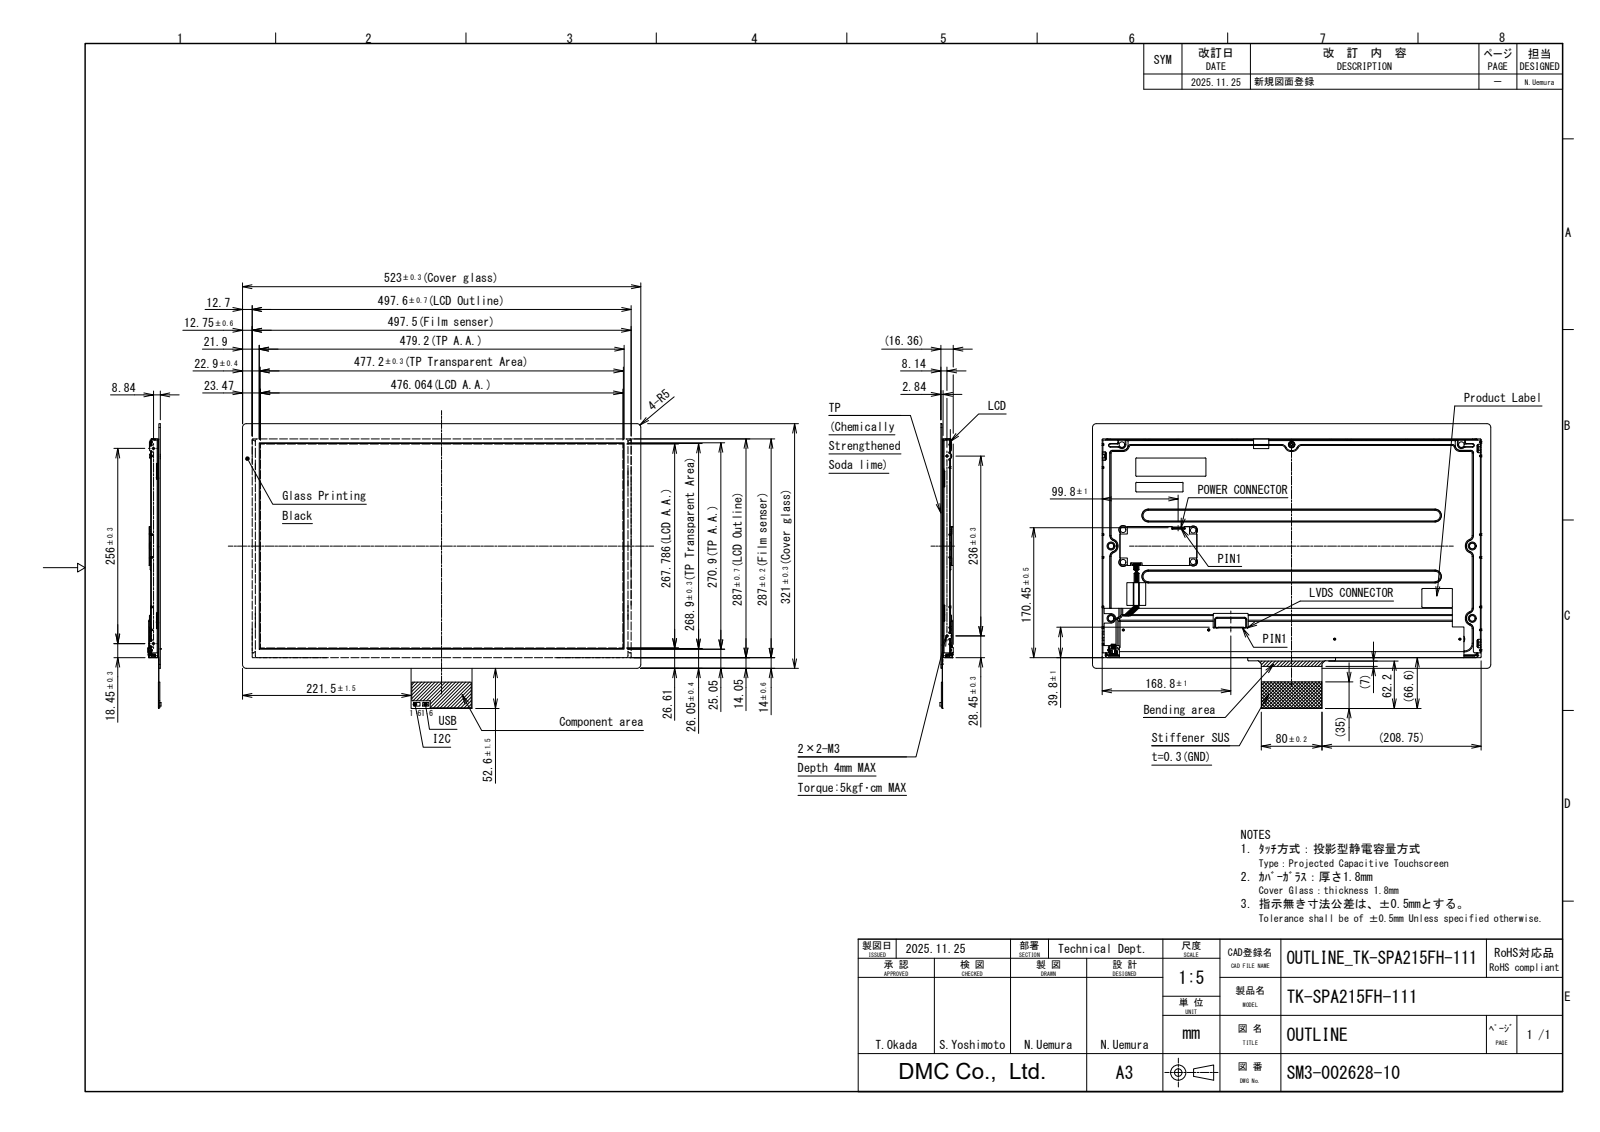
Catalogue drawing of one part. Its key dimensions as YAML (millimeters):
part_name: "TK-SPA215FH-111"
step_written_by: "Autodesk Inventor 2024 (AUTOMOTIVE_DESIGN)"
units: millimeters
bodies: {solids: 1, faces: 11736, planar: 7340, cylindrical: 3482, other: 914}
overall_size: [523, 373.6, 17.42]
volume: 765250
surface_area: 859575
round_holes:
  - {diameter: 3, count: 10}
  - {diameter: 4, count: 4}
  - {diameter: 6.5, count: 4}
  - {diameter: 0.9, count: 2}
  - {diameter: 1.1, count: 2}
  - {diameter: 2.3, count: 2}
  - {diameter: 3.6, count: 2}
  - {diameter: 6, count: 2}
  - {diameter: 8, count: 2}
  - {diameter: 2, count: 1}
round_bosses_or_shafts:
  - {diameter: 0.87, count: 47}
  - {diameter: 4.6, count: 7}
  - {diameter: 7.5, count: 6}
  - {diameter: 3, count: 6}
  - {diameter: 2.5, count: 6}
  - {diameter: 7, count: 4}
  - {diameter: 4.5, count: 4}
  - {diameter: 4, count: 4}
partial_cylinders:
  - {radius: 0.1, count: 641}
  - {radius: 0.2, count: 387}
  - {radius: 1, count: 238}
  - {radius: 0.5, count: 203}
  - {radius: 0.3, count: 160}
  - {radius: 0.15, count: 127}
  - {radius: 0.7, count: 110}
  - {radius: 0.9, count: 49}
face_to_face_distances: [0.8, 3.9, 10.44, 6.54, 5.74, 9.64, 1.8, 2.1, 0.5, 1.3]
hole_center_spacings: [5.9, 10.02, 92, 101.13, 106.12, 112.02, 165.81, 223]
